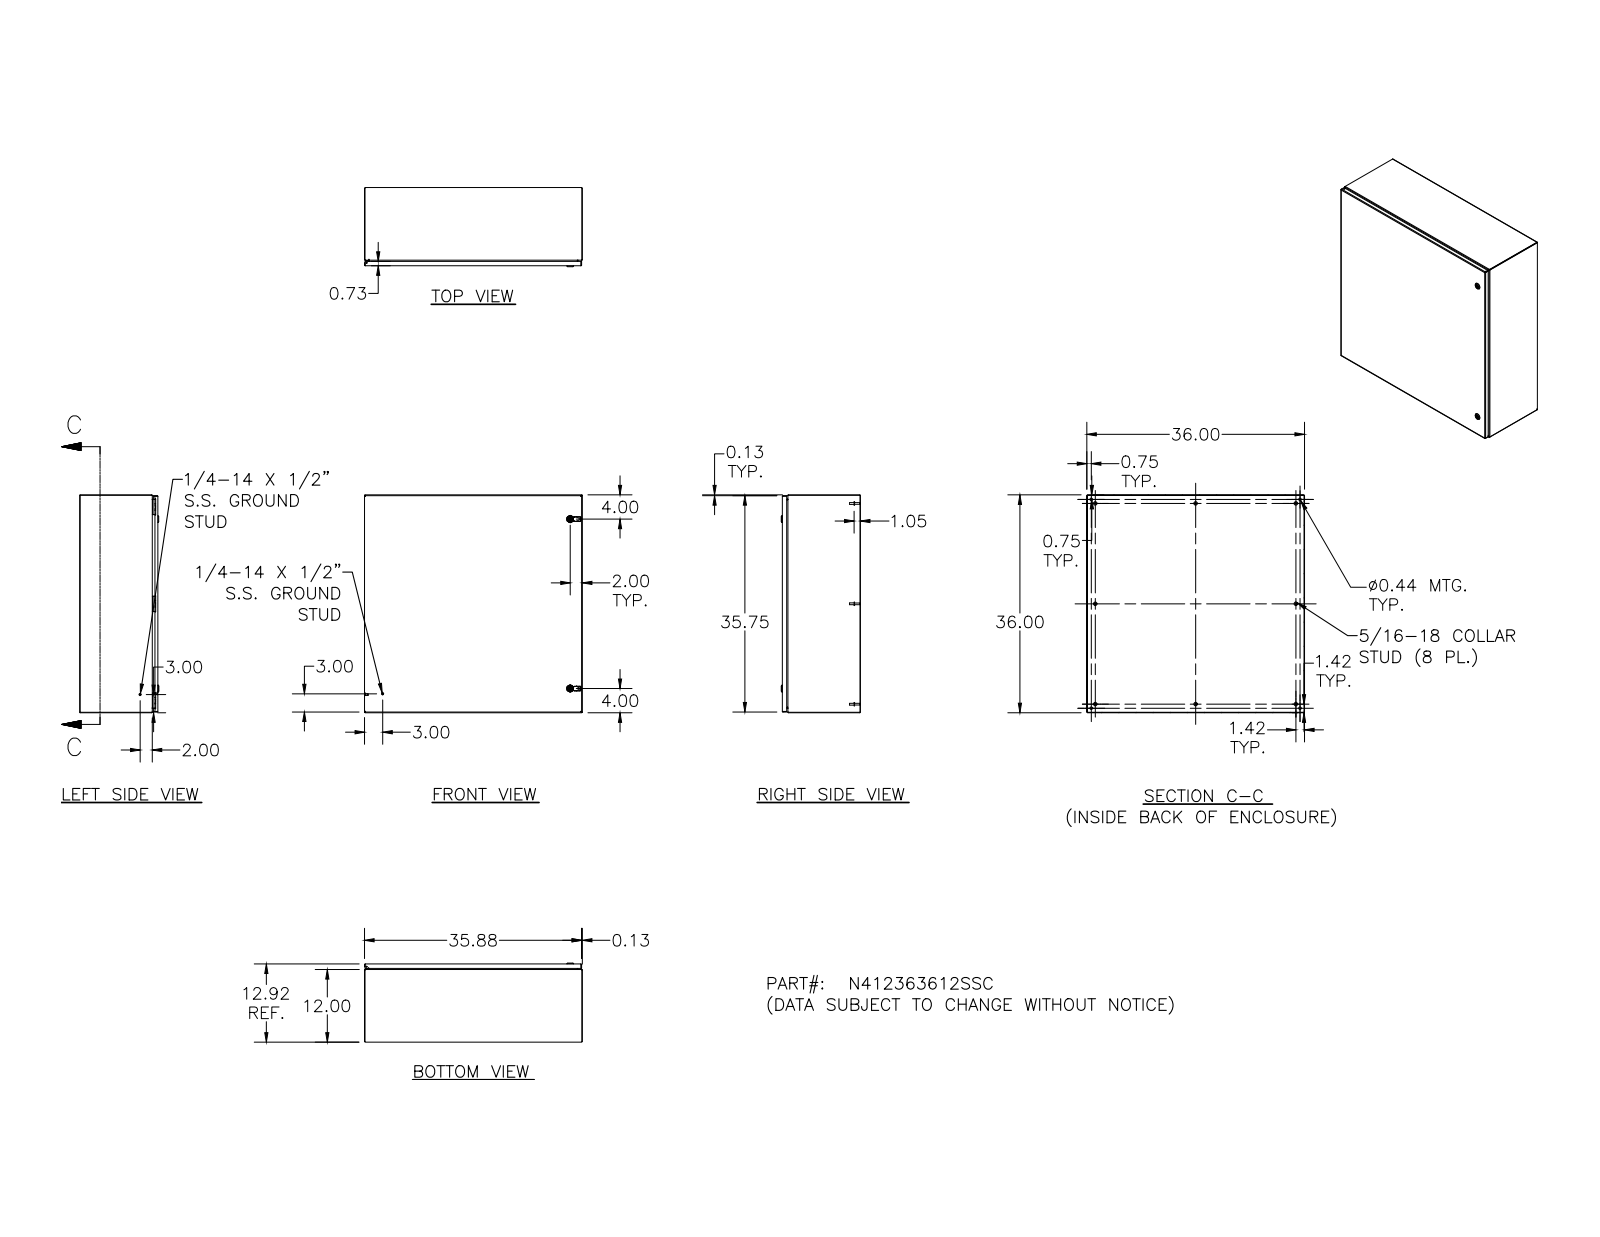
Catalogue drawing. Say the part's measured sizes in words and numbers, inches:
The part is named "N412363612SSC; N412363612SSCBTB; N4123612SSCLS; N4123612SSCRS (+8 more)". Its 3-D file was written by "Autodesk Inventor 2011 (AUTOMOTIVE_DESIGN)". It is 53 solids with 2268 faces: 863 planar, 846 cylindrical and 559 other. Overall it measures 36.127 by 36 by 14.687 inches. Its volume is 340.9 cubic inches and its surface area 9 269 square inches. Round holes: 6 of diameter 0.093, 6 of diameter 0.152, 6 of diameter 0.167, 6 of diameter 0.172, 6 of diameter 0.187, 4 of diameter 0.437, 3 of diameter 0.156, 2 of diameter 0.197, 2 of diameter 0.315, 2 of diameter 0.394, 2 of diameter 0.402, 2 of diameter 0.634. Round bosses or shafts: 14 of diameter 0.25, 8 of diameter 0.563, 8 of diameter 0.3, 8 of diameter 0.275, 6 of diameter 0.36, 6 of diameter 0.32, 6 of diameter 0.256, 6 of diameter 0.164. Partial cylindrical surfaces (rounded edges, fillets, slot ends): 54 of radius 0.012, 38 of radius 0.05, 32 of radius 0.031, 26 of radius 0.016, 24 of radius 0.125, 23 of radius 0.02, 18 of radius 0.105, 12 of radius 0.032. The main face-to-face distances are 0.074, 12.843, 35.926, 12.769, 12.917, 35.852, 36, 11.926, 0.917, 35.187. The hole center spacings are 16, 32, 16.008, 34.5, 0.5, 0.656, 0.66, 1.307.
